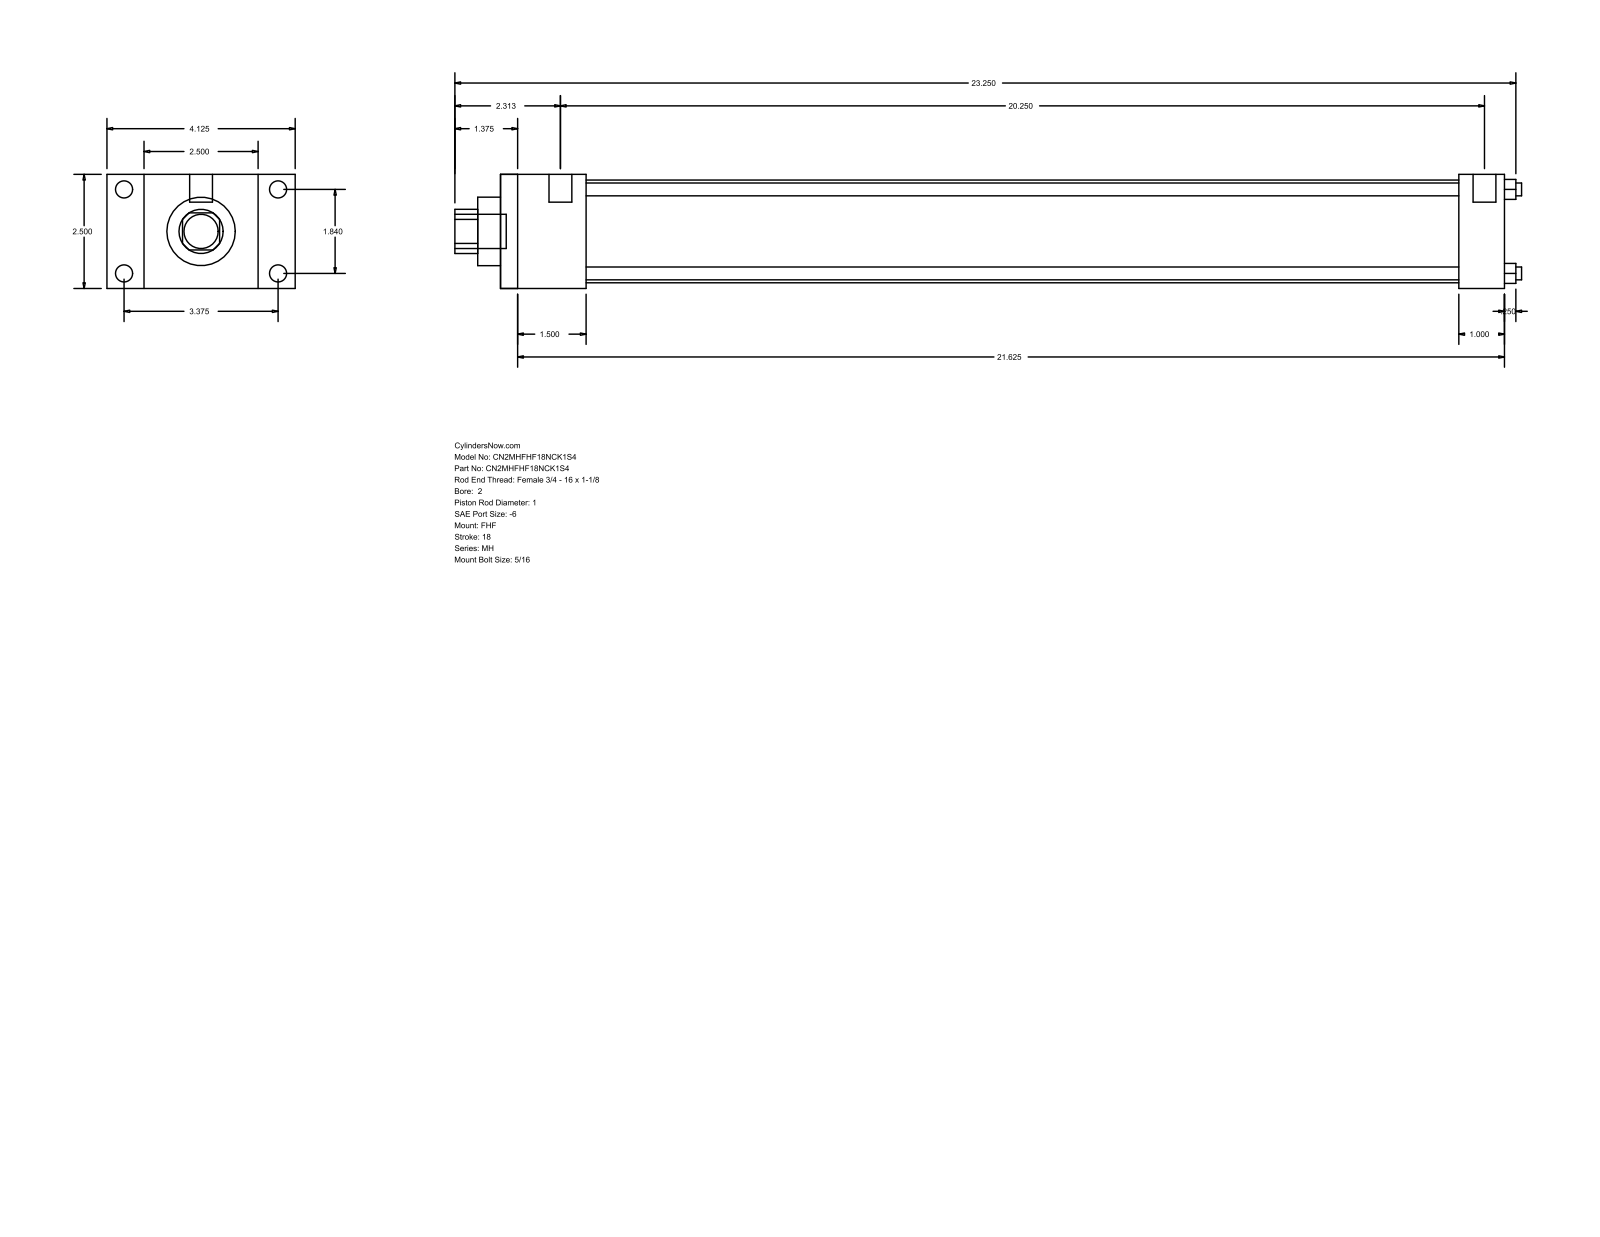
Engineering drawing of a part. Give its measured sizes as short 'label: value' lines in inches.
name: MH_FHF__0200_1
written by: GSSL Pune (CONFIG_CONTROL_DESIGN)
unit: in
bodies: 0 solids, 88 faces (60 planar, 28 cylindrical, 0 other)
size: 23.375 × 4.125 × 2.5
holes: 4× ⌀0.281, 1× ⌀1, 1× ⌀1.5, 1× ⌀2.25
bosses: 4× ⌀0.375, 4× ⌀0.219, 2× ⌀0.5, 1× ⌀0.75
rounds: 1× R0.484
face distances: 2.5, 22, 1.875, 20.125, 0.813, 3.313, 4.125, 1, 21, 19.125
hole spacings: 1.301, 1.84, 2.602
